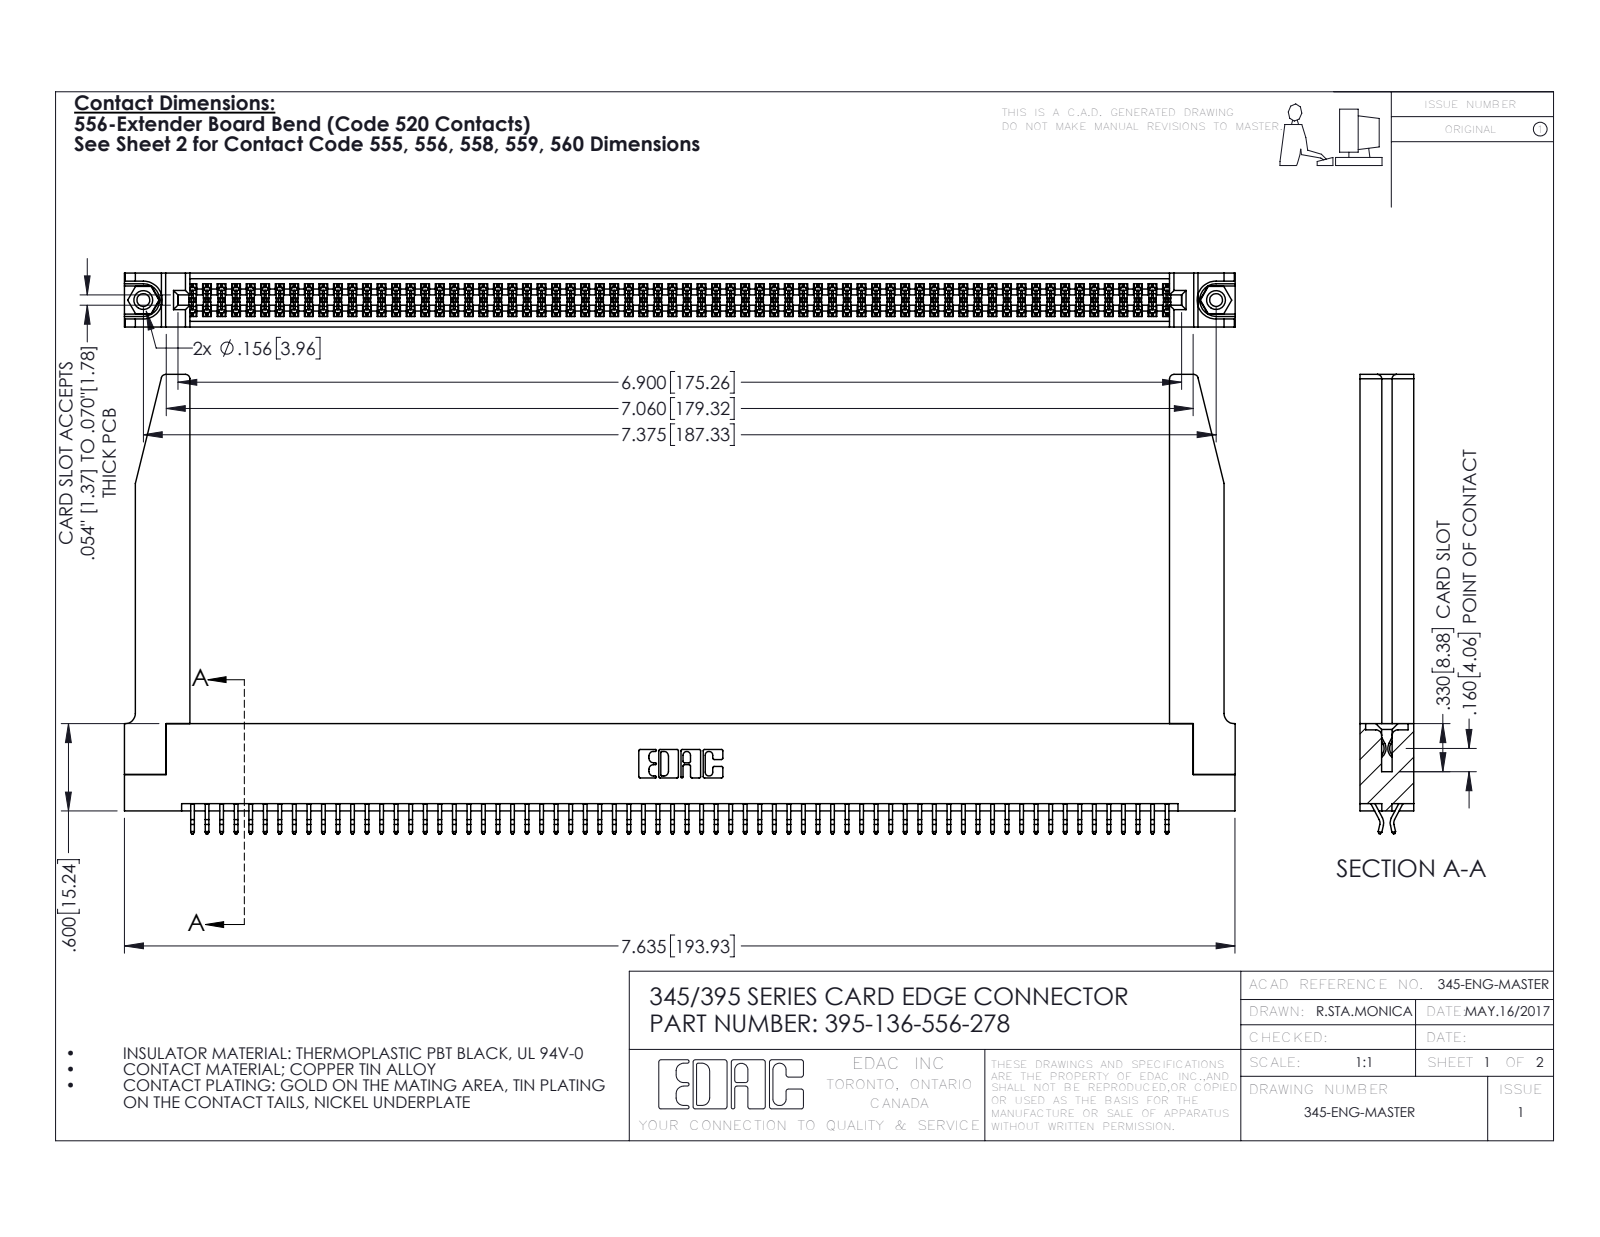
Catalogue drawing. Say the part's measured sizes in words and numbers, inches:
The part is named "395-136-556-278; 345 Part_Flush Mounting Lugs - 0.156 Dia-TH; 345-292-001_556 Tail; 345-220-078_345-220-078 (+1 more)". Its 3-D file was written by "SolidWorks 2016 (CONFIG_CONTROL_DESIGN)". It is 141 solids with 7976 faces: 5254 planar, 2670 cylindrical and 52 other. Overall it measures 7.636 by 3.157 by 0.37 inches. Its volume is 1.638 cubic inches and its surface area 54.9 square inches. Round holes: 2 of diameter 0.089, 2 of diameter 0.125, 2 of diameter 0.156, 1 of diameter 0.064. Round bosses or shafts: 2 of diameter 0.155. Partial cylindrical surfaces (rounded edges, fillets, slot ends): 204 of radius 0.006, 22 of radius 0.01, 8 of radius 0.03, 6 of radius 0.007, 6 of radius 0.031, 3 of radius 0.026, 2 of radius 0.01, 2 of radius 0.014. The main face-to-face distances are 0.072, 0.298, 0.37, 0.2, 0.025, 0.098, 0.272, 0.225, 0.175, 0.149. The hole center spacings are 0.27, 7.139, 7.375.
